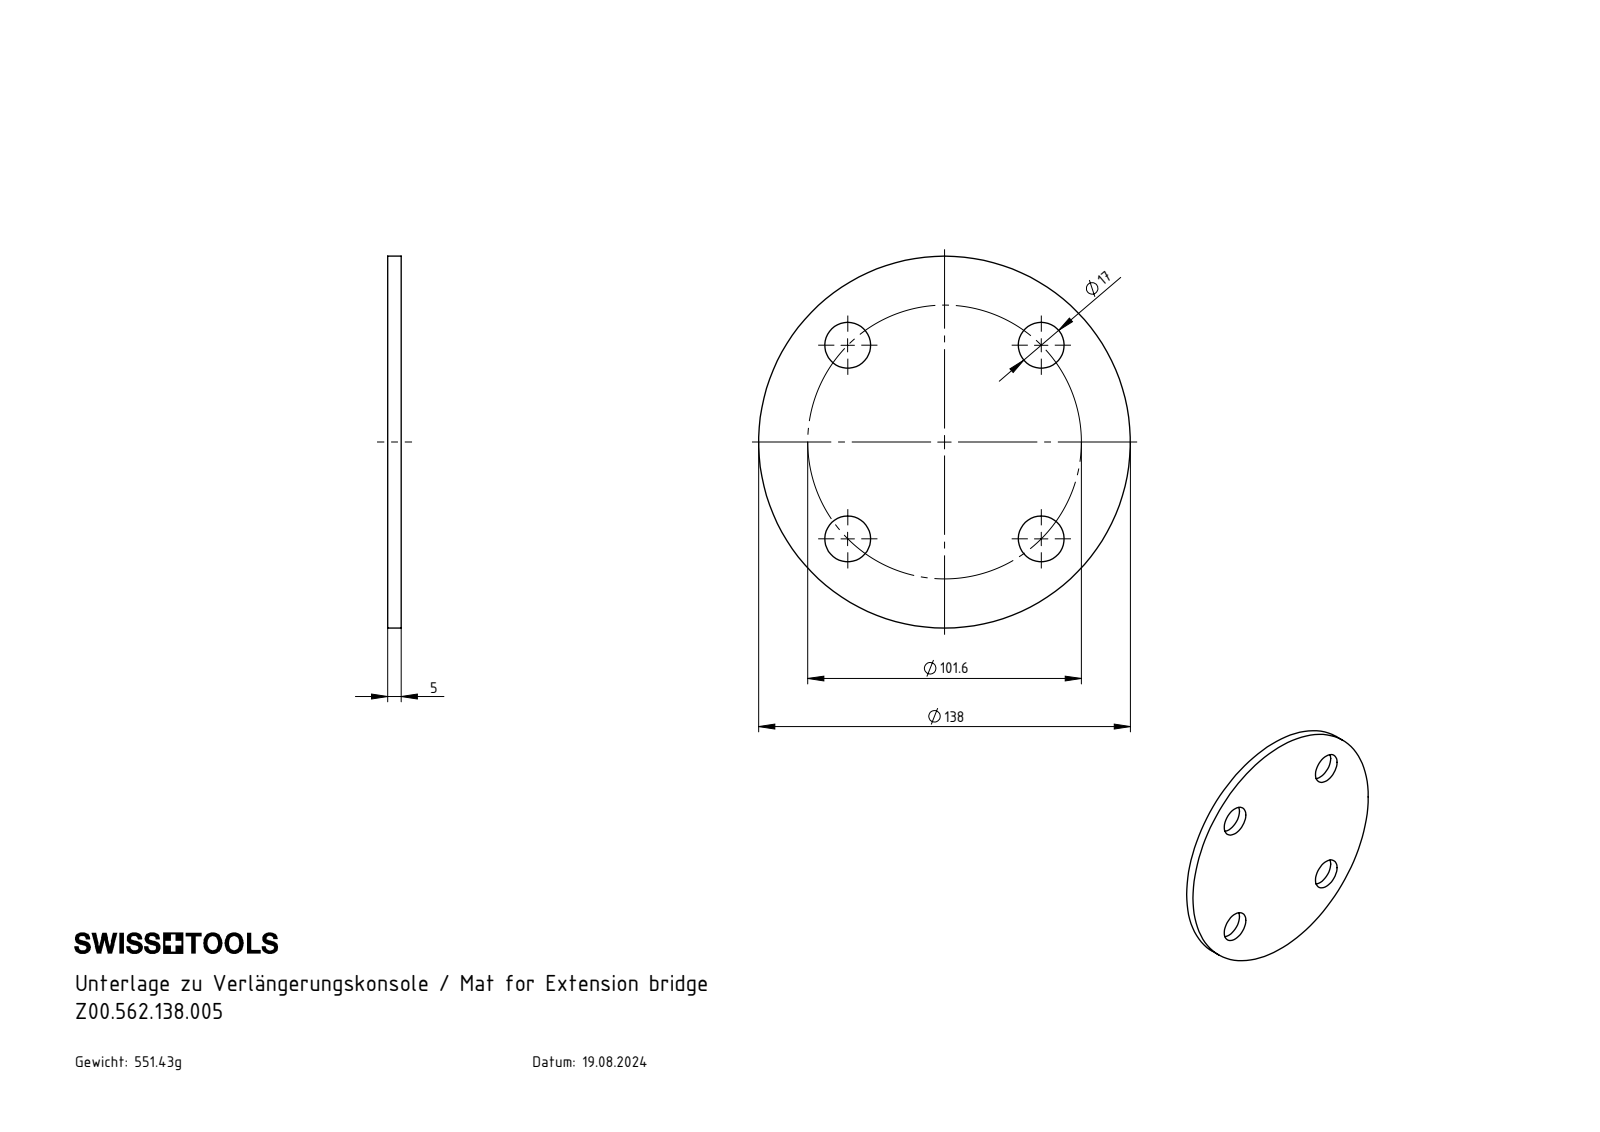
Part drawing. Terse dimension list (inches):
name: Z00.562.138.005
written by: SolidWorks 2022 (CONFIG_CONTROL_DESIGN)
unit: in
bodies: 1 solid, 12 faces (2 planar, 10 cylindrical, 0 other)
size: 5.433 × 5.433 × 0.197
volume: 4.287 in³; area: 48.57 in²
holes: 4× ⌀0.669
bosses: 1× ⌀5.433
face distances: 0.197
hole spacings: 2.828, 4
